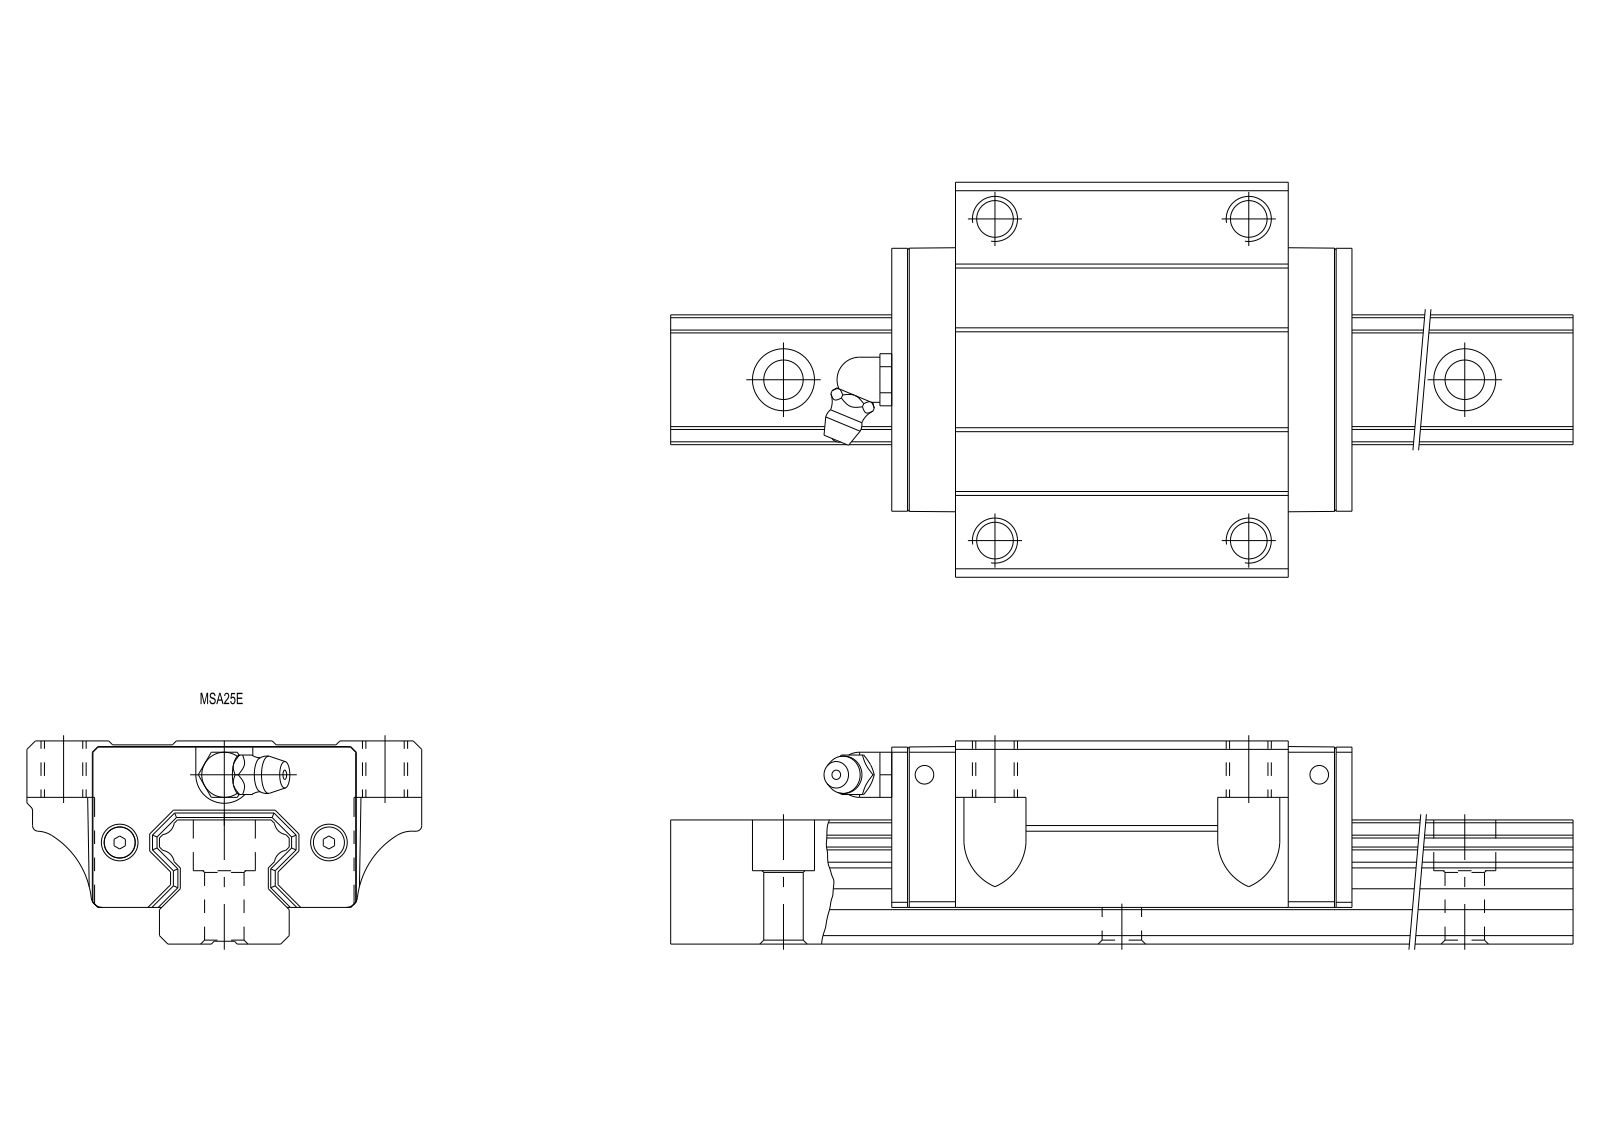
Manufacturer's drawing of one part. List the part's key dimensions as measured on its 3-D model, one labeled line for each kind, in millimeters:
STEP written by: Kubotek KeyCreator V6.5.2 (0407) (CONFIG_CONTROL_DESIGN)
Units: millimetres
Bodies: 3 solids, 246 faces (153 planar, 76 cylindrical, 17 other)
Overall size (bounding box): 220 × 70 × 36
Volume: 194 726 mm³ · Surface area: 45 240 mm²
Round holes (diameter × count): ⌀7 ×4, ⌀8 ×4, ⌀11 ×4, ⌀3.25 ×2, ⌀6.5 ×2
Round bosses / shafts (diameter × count): ⌀8 ×1
Partial cylindrical surfaces — rounded edges, fillets, slot ends (radius × count): R1 ×4, R2.65 ×4, R5.5 ×4, R2 ×2, R5 ×2, R15 ×2, R5.05 ×1
Main face-to-face distances: 22, 14, 36, 6.5, 3.77, 19.23, 34.8, 15.5, 29.5, 46.5
Hole centre spacings: 29.47, 59.74, 73.27, 116.05, 60, 45, 57, 72.62
